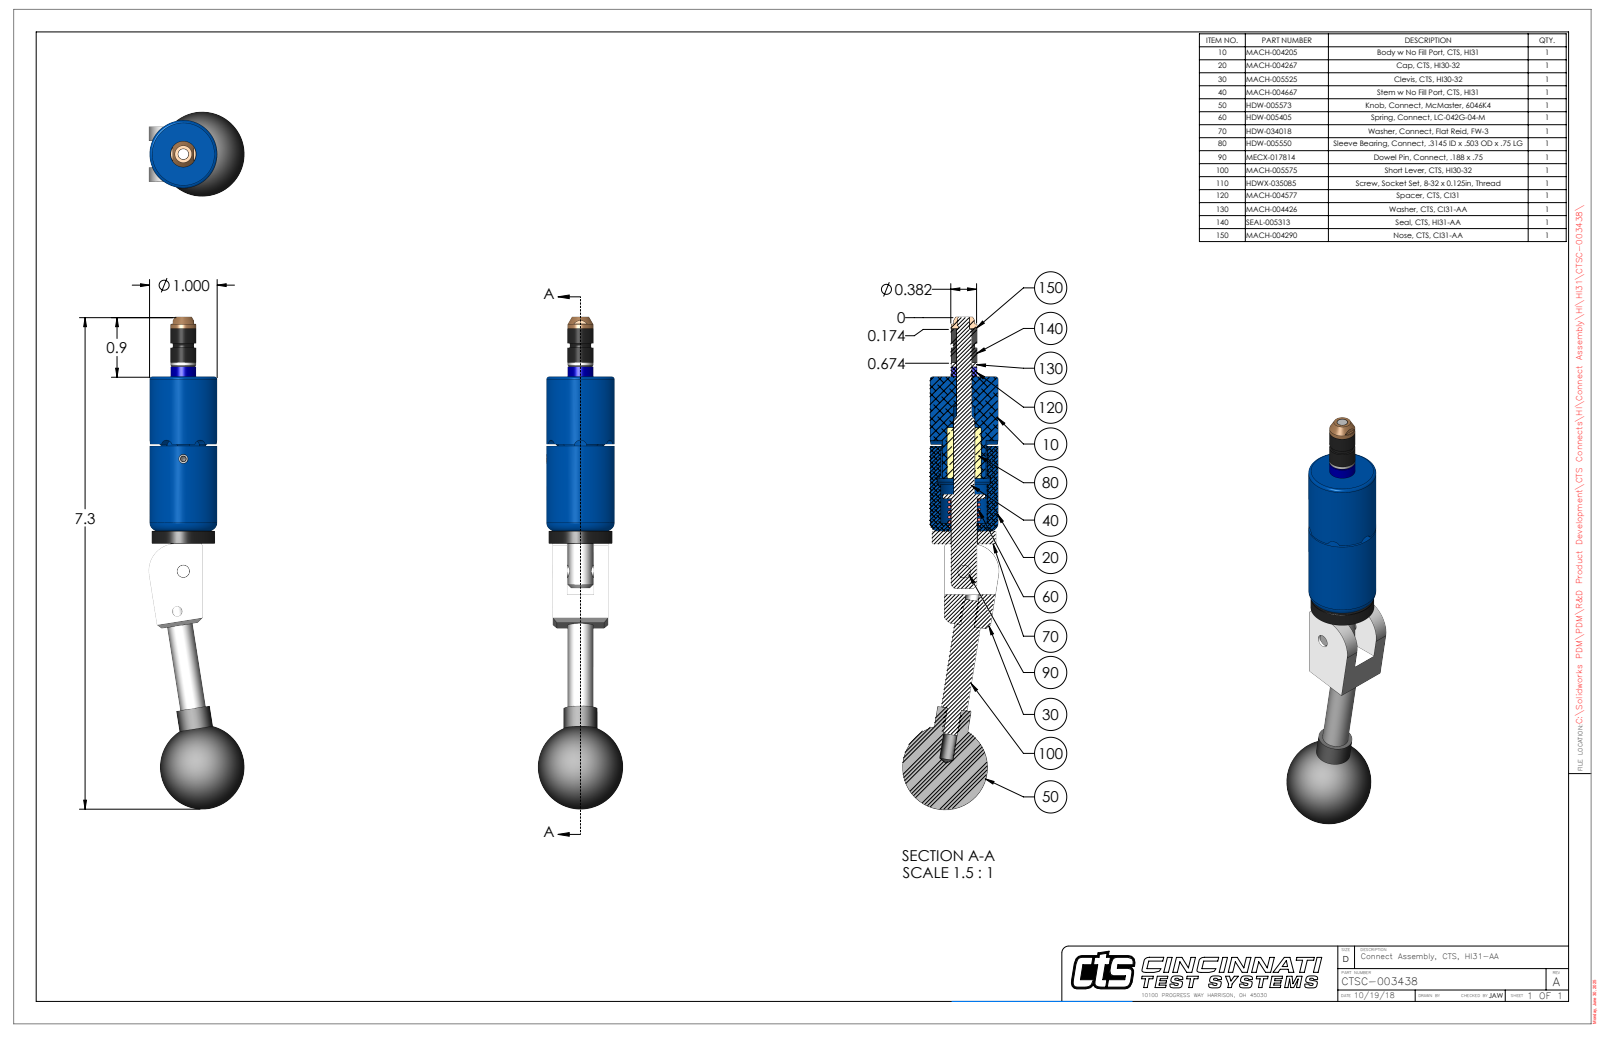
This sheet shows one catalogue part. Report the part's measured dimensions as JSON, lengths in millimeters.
{"part_name": "CTSC-003438", "step_written_by": "SolidWorks 2023 (AUTOMOTIVE_DESIGN)", "units": "millimeters", "bodies": {"solids": 10, "faces": 253, "planar": 98, "cylindrical": 98, "other": 57}, "overall_size": [184.6, 36, 31.8], "volume_mm3": 61420, "surface_area_mm2": 19350, "round_holes": [[5.1, 2], [3.5, 1], [3.8, 1], [4, 1], [4.8, 1], [5.5, 1], [5.8, 1], [5.8, 1], [9.8, 1], [10, 1]], "round_bosses_or_shafts": [[25.4, 1], [23.8, 1], [12.7, 1], [9.8, 1], [9.7, 1], [9.7, 1], [9.6, 1], [9.5, 1]], "partial_cylinders_radius": [[2.4, 6], [0.7, 2], [8.7, 1], [10.2, 1], [12, 1]], "face_to_face_distances": [5.3, 15.3, 20.6, 4.7, 57.9, 62.6, 9.9, 26, 31.8, 36.6], "hole_center_spacings": [15.2, 42.1, 57.2]}
